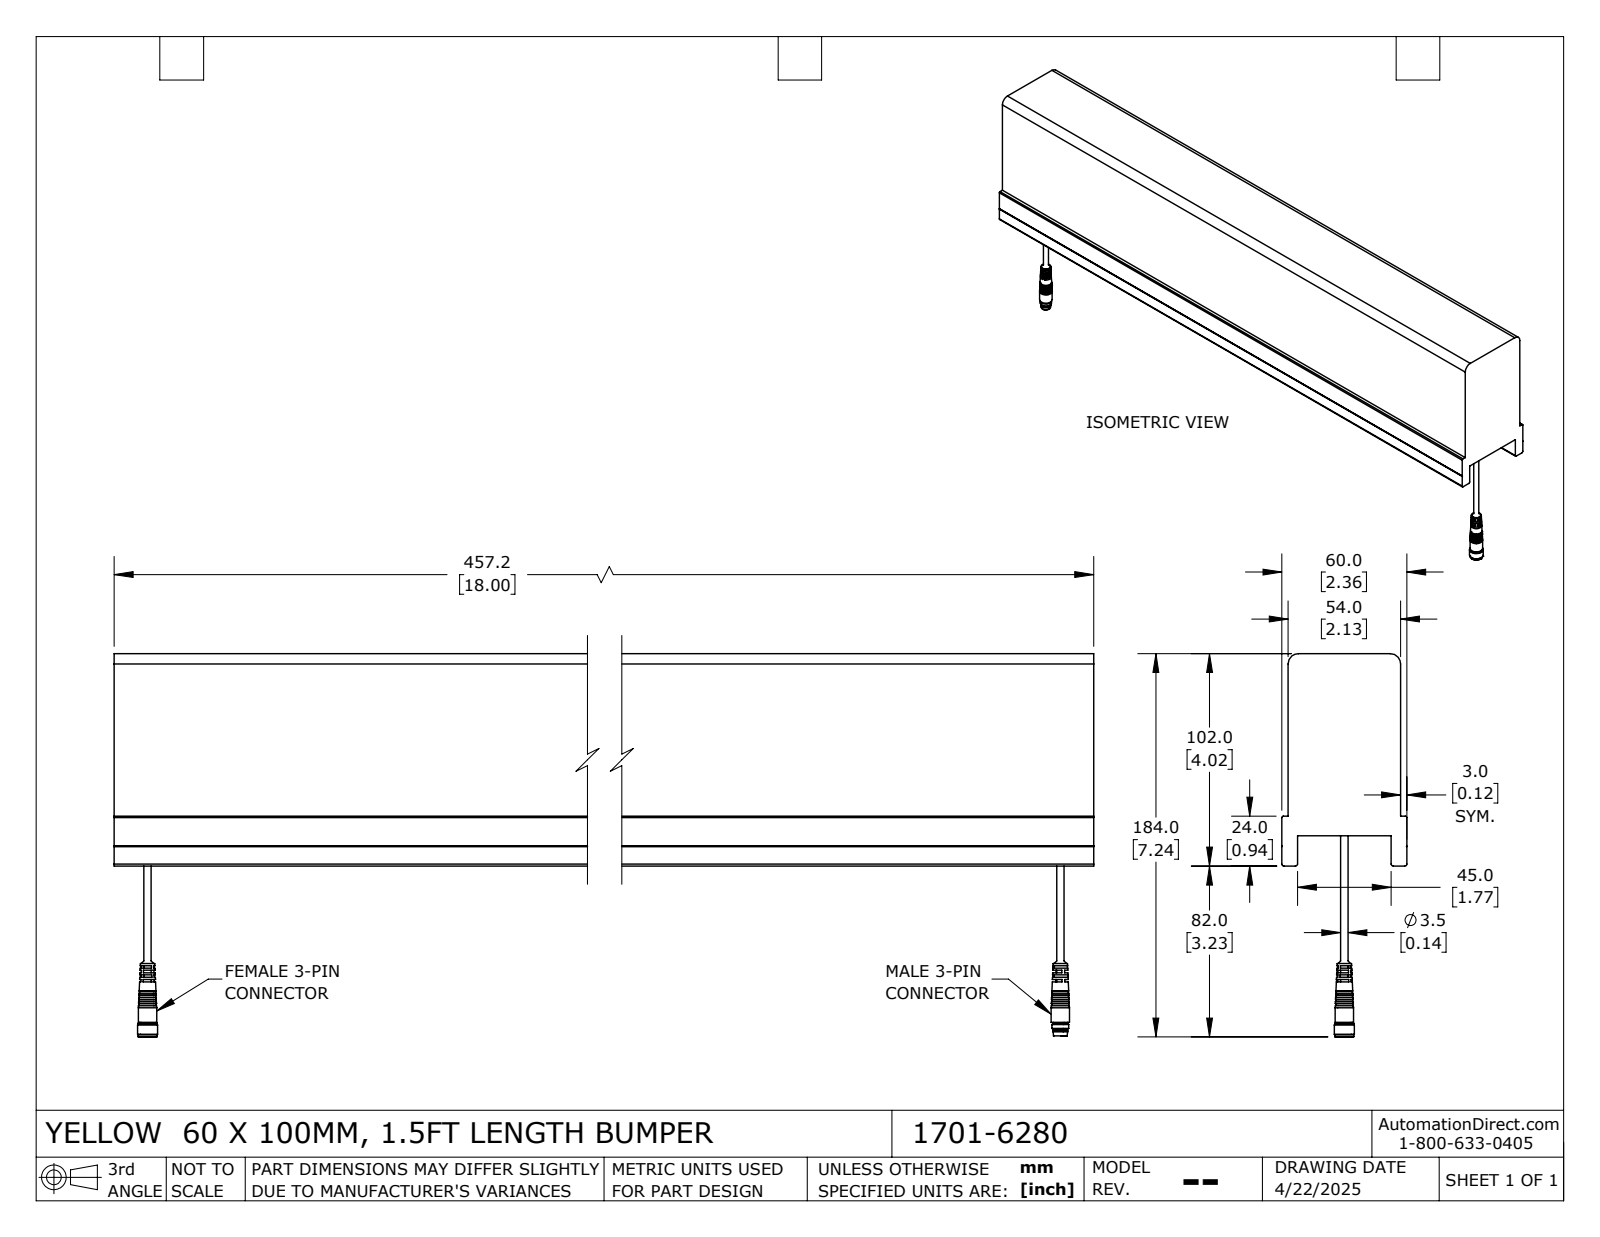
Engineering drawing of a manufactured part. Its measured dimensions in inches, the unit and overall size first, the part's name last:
Units: inches
Overall size (bounding box): 18 × 7.244 × 2.362
Round holes (diameter × count): ⌀0.063 ×3, ⌀0.134 ×2, ⌀0.228 ×1, ⌀0.232 ×1, ⌀0.272 ×1, ⌀0.283 ×1
Round bosses / shafts (diameter × count): ⌀0.047 ×16, ⌀0.031 ×4, ⌀0.039 ×3, ⌀0.346 ×2, ⌀0.138 ×2, ⌀0.378 ×1, ⌀0.354 ×1, ⌀0.315 ×1
Main face-to-face distances: 2.126, 3.445, 0.118, 2.244, 0.295, 2.067, 0.177, 1.949, 2.362, 1.772
Hole centre spacings: 0.069, 0.098, 16.789, 0.138, 16.691, 16.74
Volume: 139.4 in³ · Surface area: 269.6 in²
Bodies: 20 solids, 294 faces (138 planar, 59 cylindrical, 97 other)
Part name (STEP PRODUCT): 1701-3700
STEP written by: SolidWorks 2018 (AUTOMOTIVE_DESIGN)
